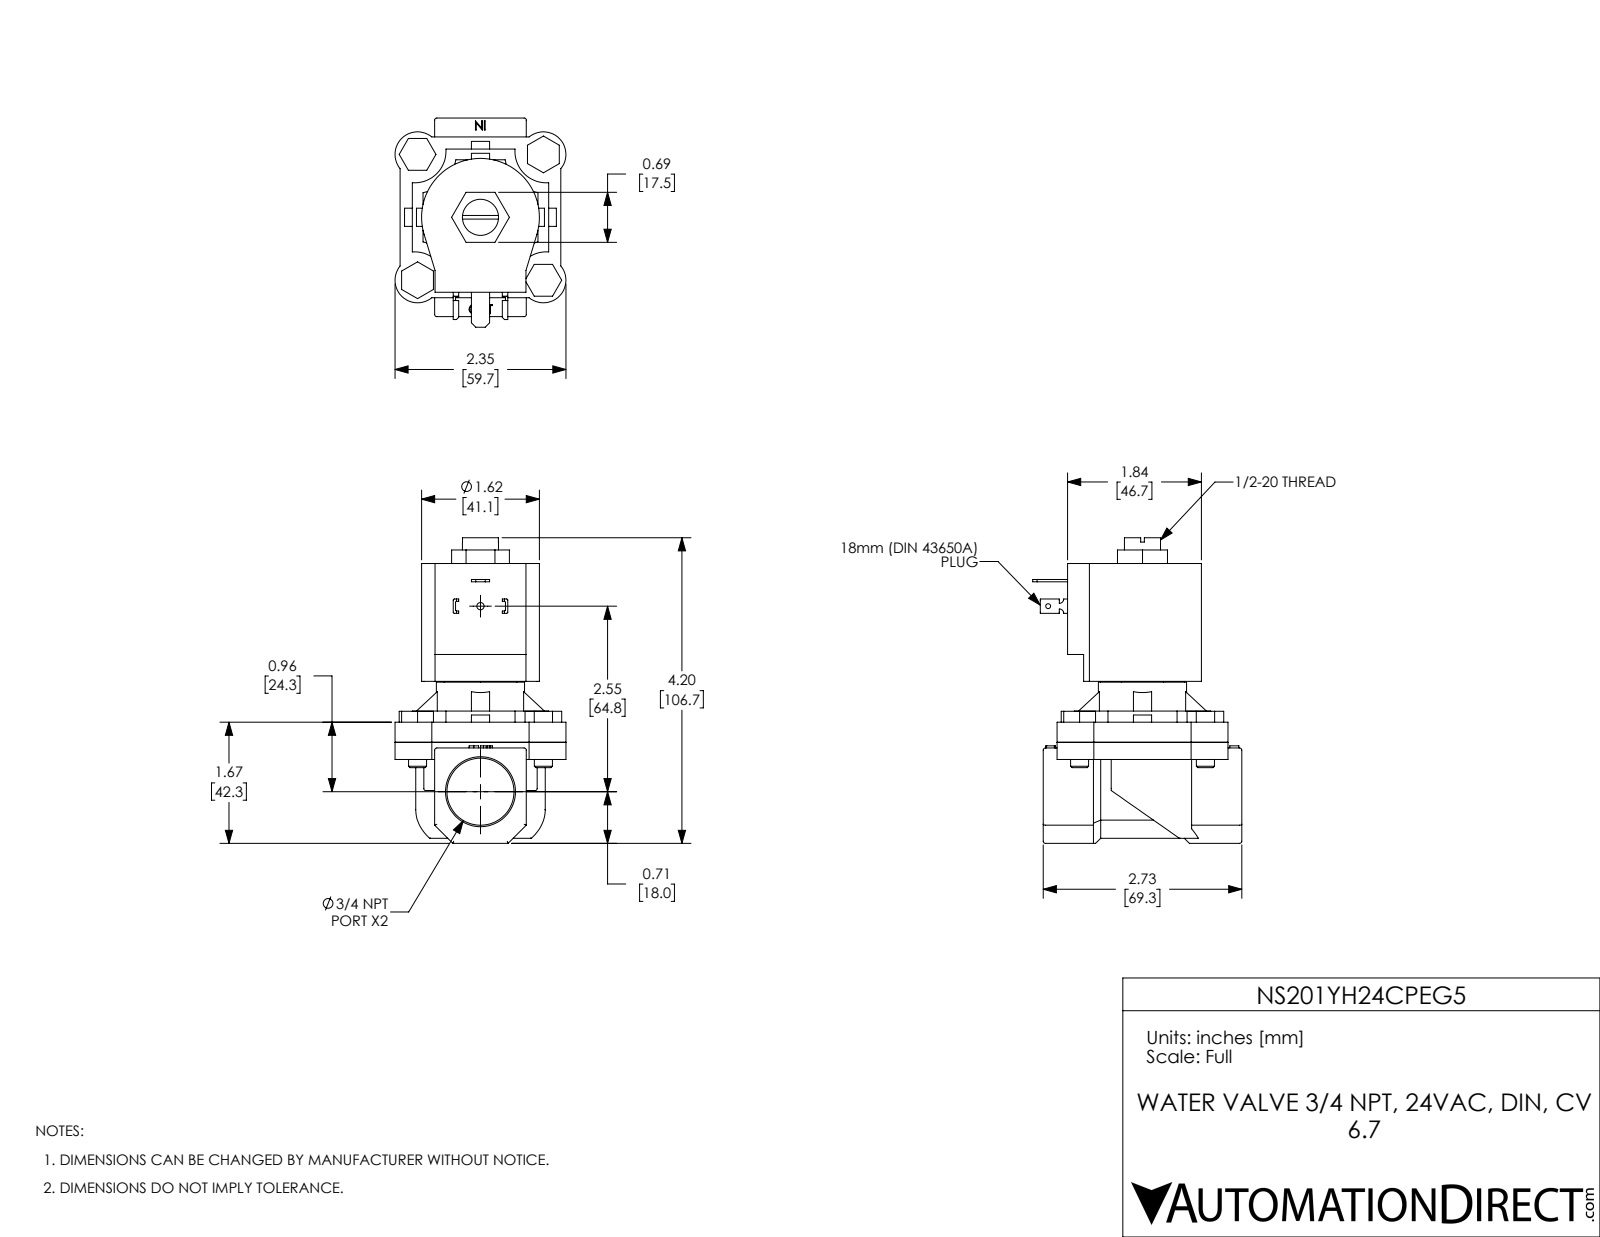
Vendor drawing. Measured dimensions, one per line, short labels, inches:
name: NS201YH24CPEG5
written by: SolidWorks 2024 (CONFIG_CONTROL_DESIGN)
unit: in
bodies: 11 solids, 387 faces (241 planar, 113 cylindrical, 33 other)
size: 4.2 × 2.875 × 2.35
volume: 10.6 in³; area: 70.72 in²
holes: 4× ⌀0.25, 1× ⌀0.067, 1× ⌀0.1, 1× ⌀0.496, 1× ⌀0.512, 1× ⌀0.922, 1× ⌀1.155
bosses: 4× ⌀0.248, 1× ⌀1.213
rounds: 15× R0.03, 8× R0.015, 4× R0.31, 4× R0.432, 4× R0.579, 2× R0.06, 1× R0.81, 1× R0.89
face distances: 0.276, 2.457, 2.181, 0.236, 0.512, 2.693, 0.475, 1.735, 1.26, 2.21
hole spacings: 1.223, 1.73, 2.446, 2.55
